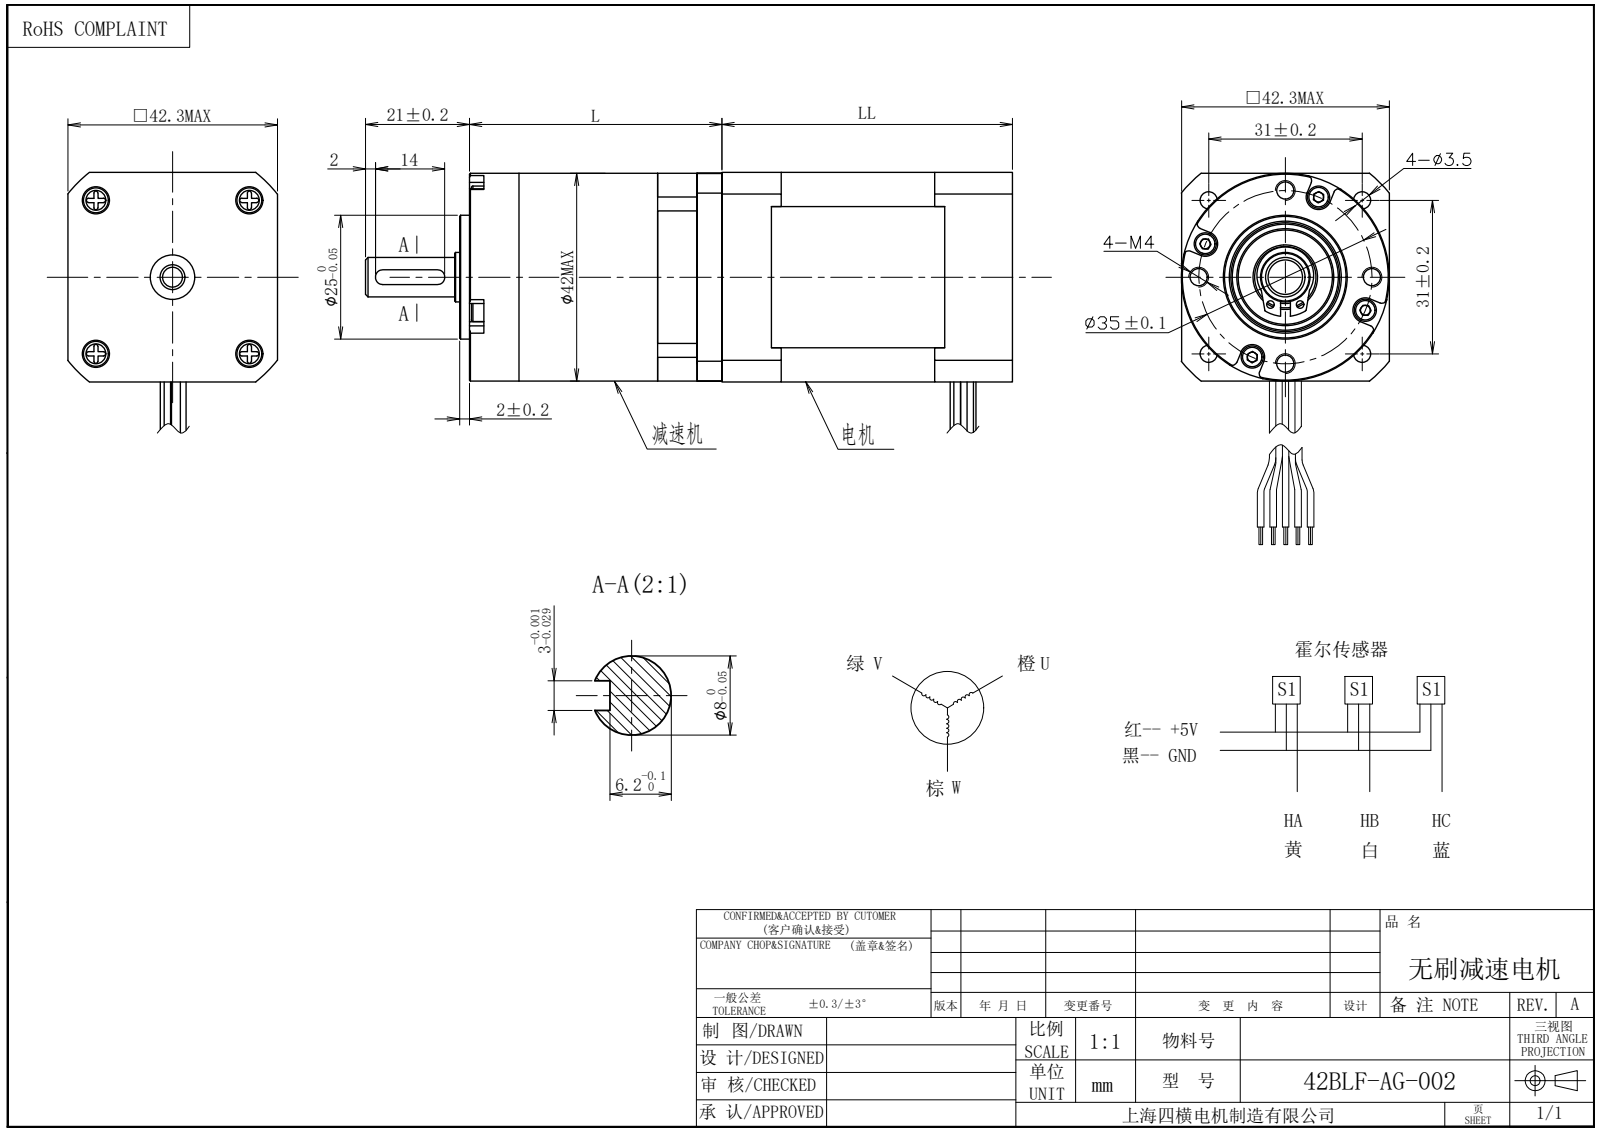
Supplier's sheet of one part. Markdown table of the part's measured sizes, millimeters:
| quantity | value |
| --- | --- |
| part name | 42A-D19; PLA36-013齿圈; 42B-D19; M3螺钉 (+8 more) |
| STEP written by | SolidWorks 2020 (AUTOMOTIVE_DESIGN) |
| units | millimeters |
| bodies | 28 solids, 622 faces (243 planar, 284 cylindrical, 95 other) |
| overall size | 130.7 × 75.89 × 60.28 |
| volume | 166 105 mm³ |
| surface area | 52 637 mm² |
| round holes (diameter × count) | 2.9 × 8, 3.3 × 8, 5 × 7, 2.5 × 6, 3.5 × 4, 5.5 × 4, 3 × 3, 1.5 × 2, 6 × 1, 9 × 1, 9.3 × 1, 10 × 1 |
| round bosses / shafts (diameter × count) | 1.3 × 5, 5 × 4, 4.5 × 4, 3 × 4, 2.5 × 4, 1.8 × 3, 42 × 1, 25.9 × 1 |
| partial cylindrical surfaces (radius × count) | 0.41 × 8, 0.44 × 8, 1 × 8, 2.25 × 4, 2.5 × 4, 0.2 × 2, 0.5 × 2, 1.5 × 2 |
| main face-to-face distances | 10, 51, 42.3, 41, 45, 13, 23, 35, 58, 86 |
| hole center spacings | 15.63, 17.5, 24.75, 15.7, 36.91, 25.1, 25.11, 0.5 |
